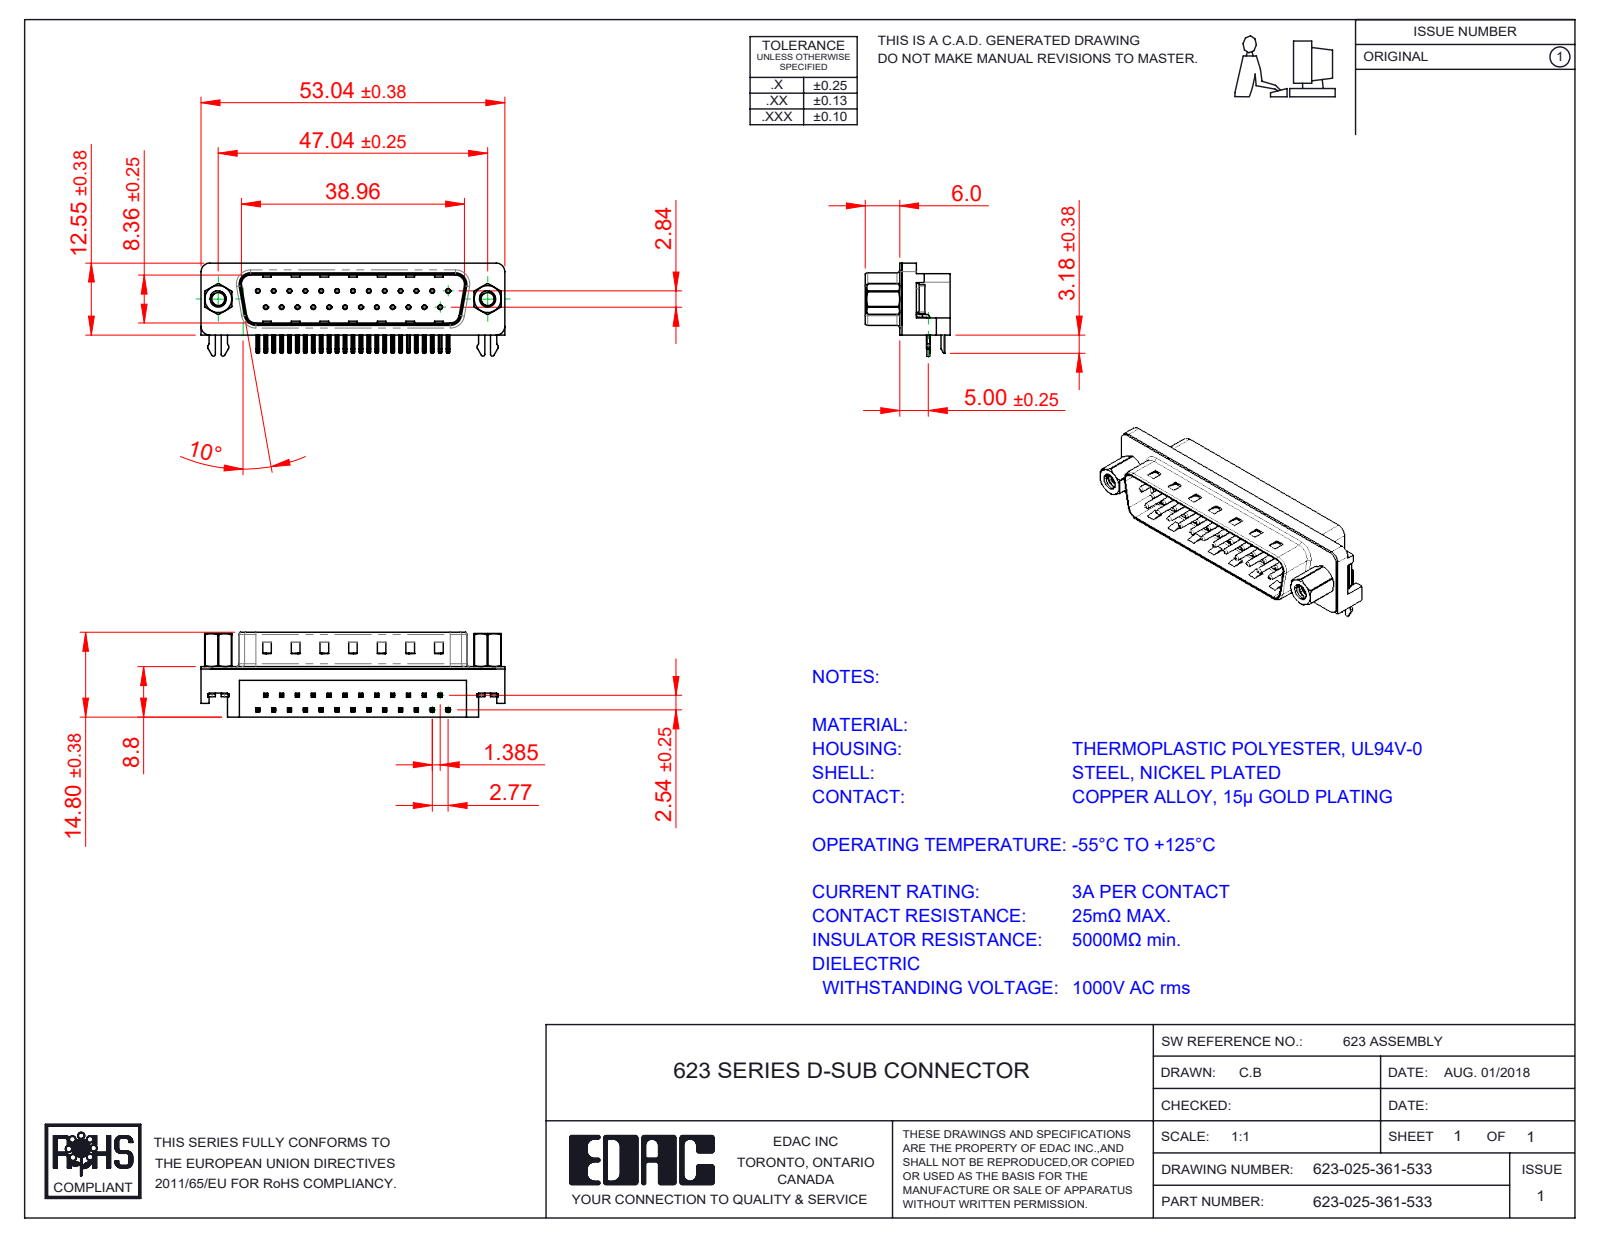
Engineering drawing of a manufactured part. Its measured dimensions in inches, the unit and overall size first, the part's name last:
Units: inches
Overall size (bounding box): 2.088 × 0.64 × 0.583
Round holes (diameter × count): ⌀0.014 ×25, ⌀0.031 ×25, ⌀0.089 ×2, ⌀0.09 ×2, ⌀0.157 ×2, ⌀0.189 ×2, ⌀0.197 ×2
Round bosses / shafts (diameter × count): ⌀0.03 ×25, ⌀0.193 ×2, ⌀0.187 ×2, ⌀0.154 ×2, ⌀0.11 ×2
Partial cylindrical surfaces — rounded edges, fillets, slot ends (radius × count): R0.01 ×108, R0.005 ×50, R0.02 ×14, R0.039 ×8, R0.059 ×7, R0.013 ×4, R0.035 ×4, R0.063 ×4
Main face-to-face distances: 0.016, 0.331, 0.083, 0.067, 0.345, 0.412, 0.428, 0.346, 0.407, 0.232
Hole centre spacings: 0.124, 0.109, 0.436, 0.218, 0.327, 0.198, 0.545, 0.294
Volume: 0.302 in³ · Surface area: 11.24 in²
Bodies: 33 solids, 2409 faces (1455 planar, 721 cylindrical, 233 other)
Part name (STEP PRODUCT): 623 Shell_25 Socket; 623 Contact Bottom; 623 4-40 Threaded Rivet; 623 2 Prong Board Lock (+4 more)
STEP written by: SolidWorks 2016 (CONFIG_CONTROL_DESIGN)
